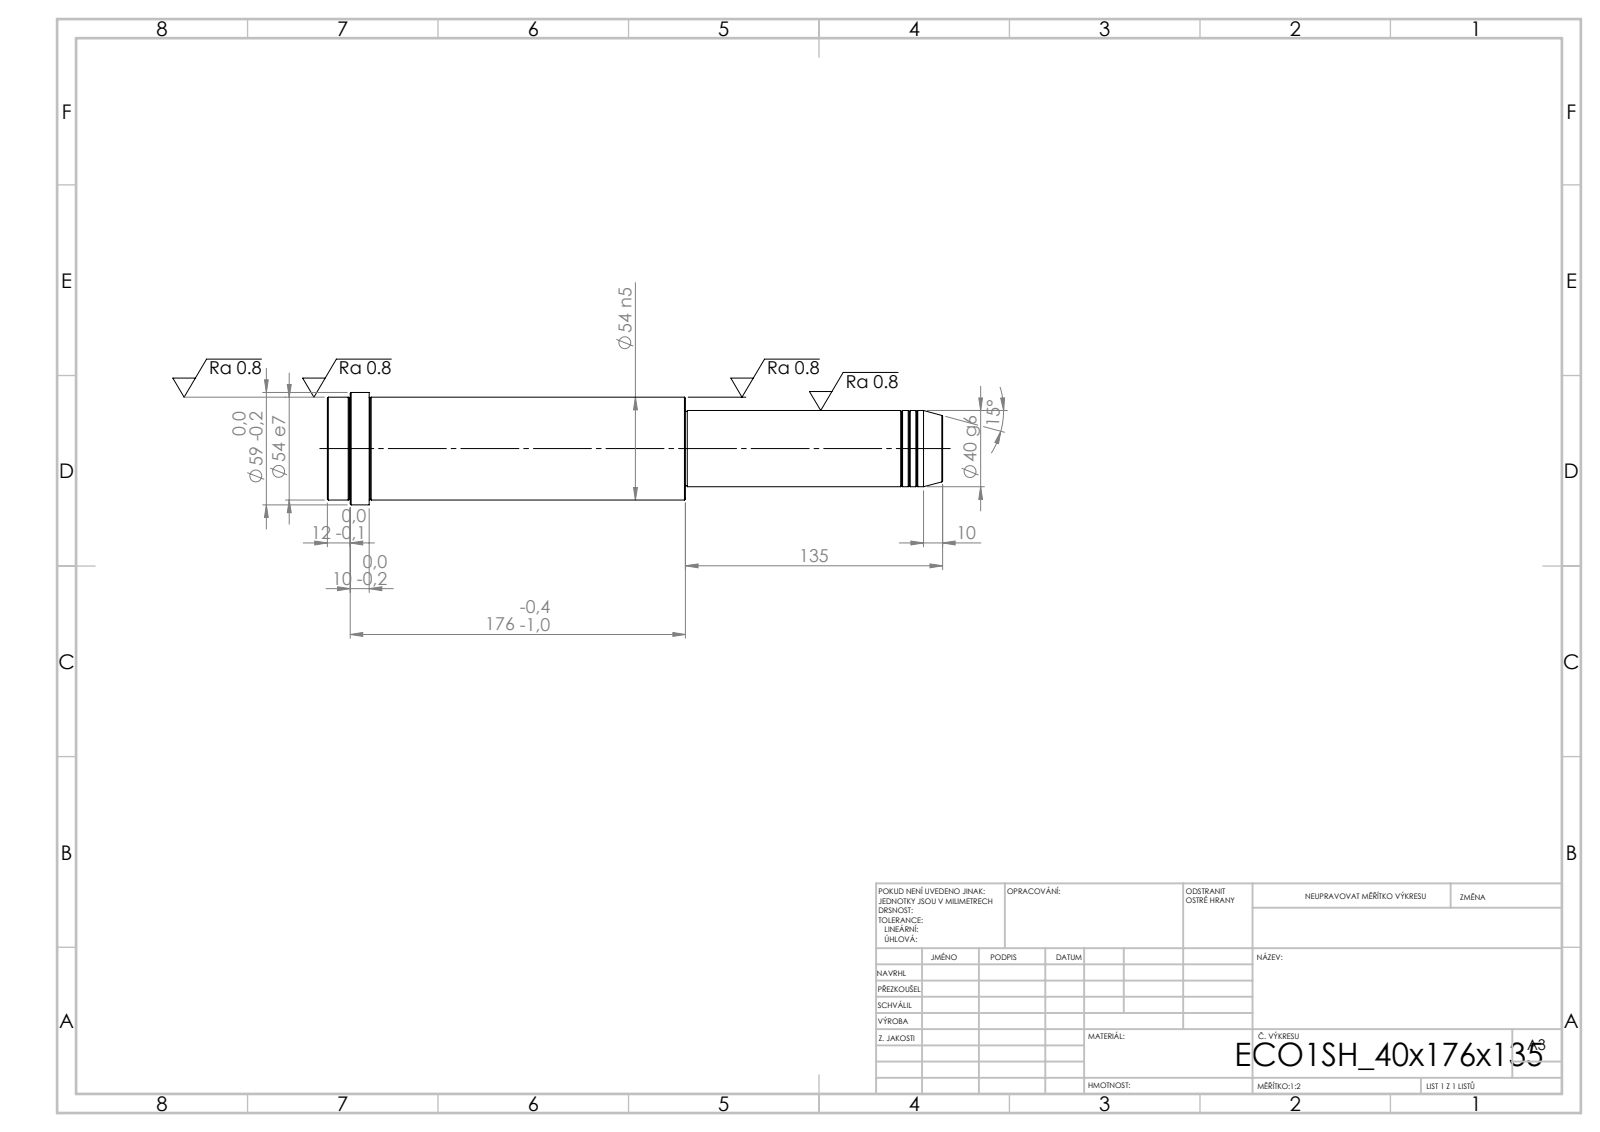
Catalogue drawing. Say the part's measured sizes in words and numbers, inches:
Its 3-D file was written by "SolidWorks 2019 (CONFIG_CONTROL_DESIGN)". It is 1 solid with 52 faces: 6 planar, 16 cylindrical and 30 other. Overall it measures 12.717 by 2.323 by 2.323 inches. Its volume is 36.77 cubic inches and its surface area 84.43 square inches. Round bosses or shafts: 1 of diameter 2.323, 1 of diameter 2.126, 1 of diameter 1.575, 1 of diameter 1.535. The main face-to-face distances are 7.402, 5.315, 12.717, 11.85, 6.535, 0.866, 12.244, 6.929, 0.394, 0.472.
